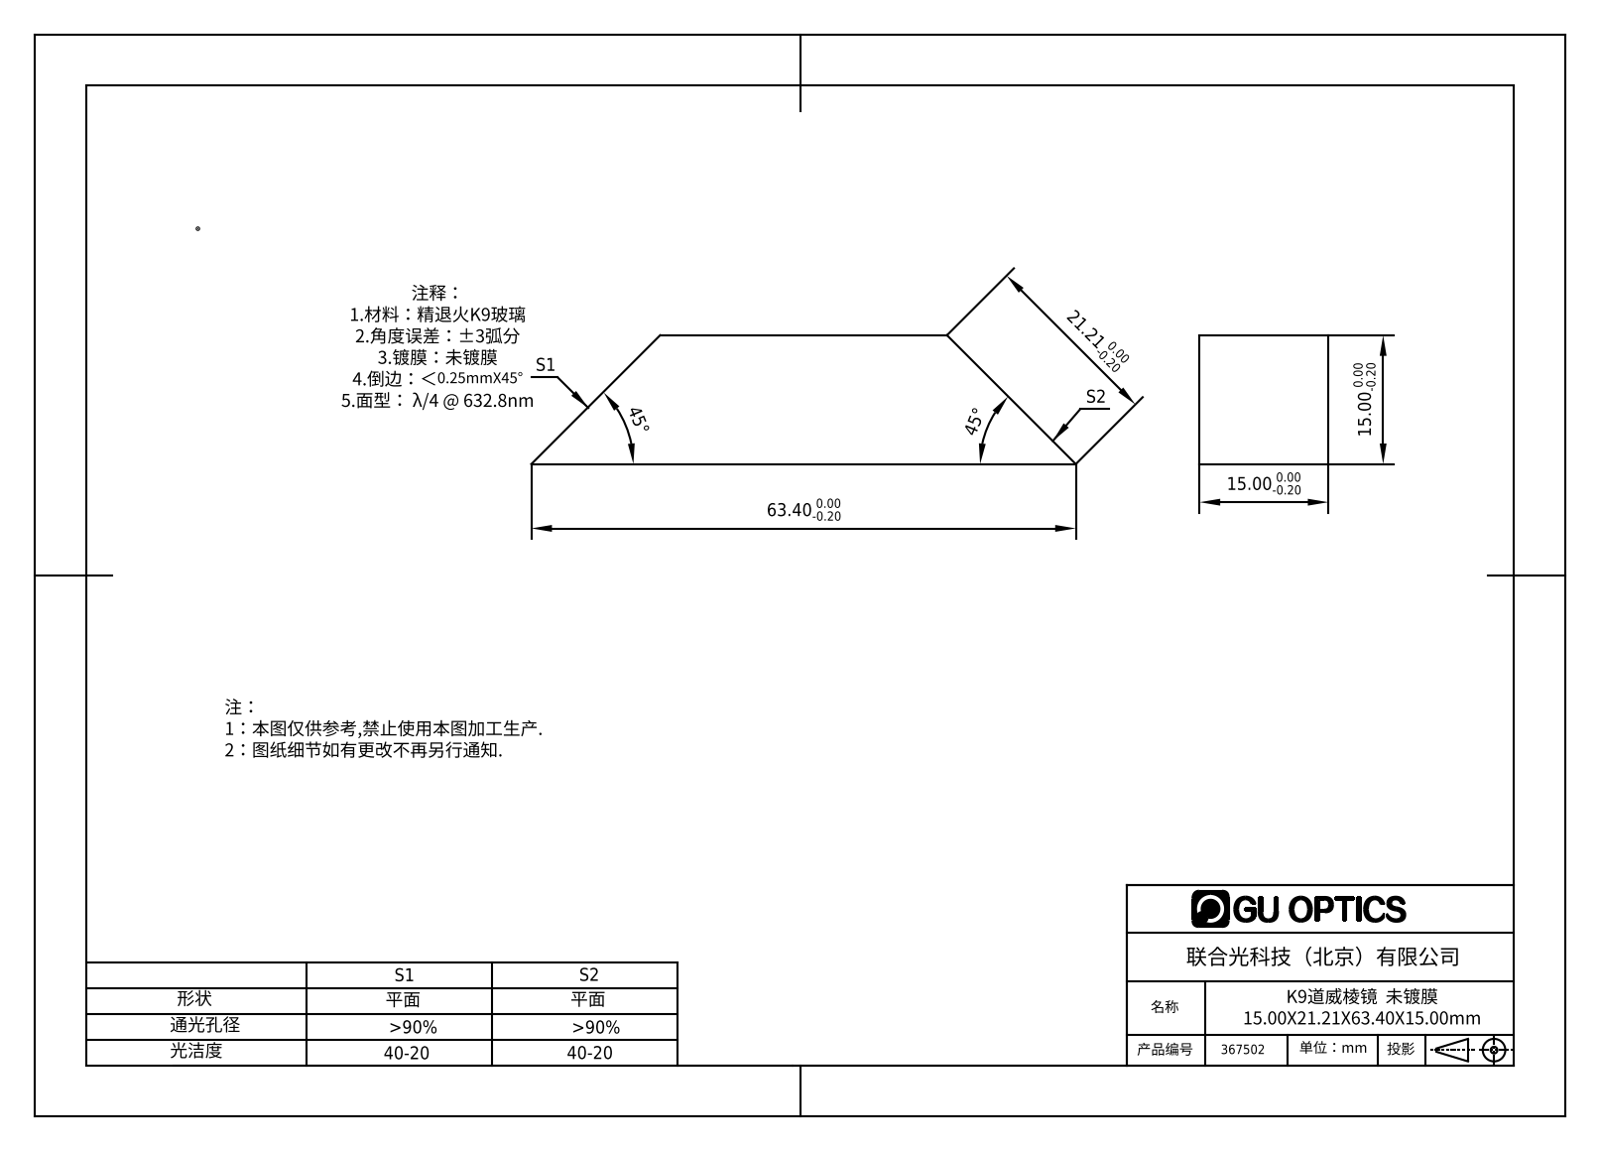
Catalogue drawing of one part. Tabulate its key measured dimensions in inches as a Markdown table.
| quantity | value |
| --- | --- |
| part name | 367502 |
| STEP written by | SolidWorks 2016 (CONFIG_CONTROL_DESIGN) |
| units | inches |
| bodies | 1 solid, 6 faces (6 planar, 0 cylindrical, 0 other) |
| overall size | 2.496 × 0.591 × 0.591 |
| volume | 0.665 in³ |
| surface area | 5.487 in² |
| main face-to-face distances | 0.591 |
